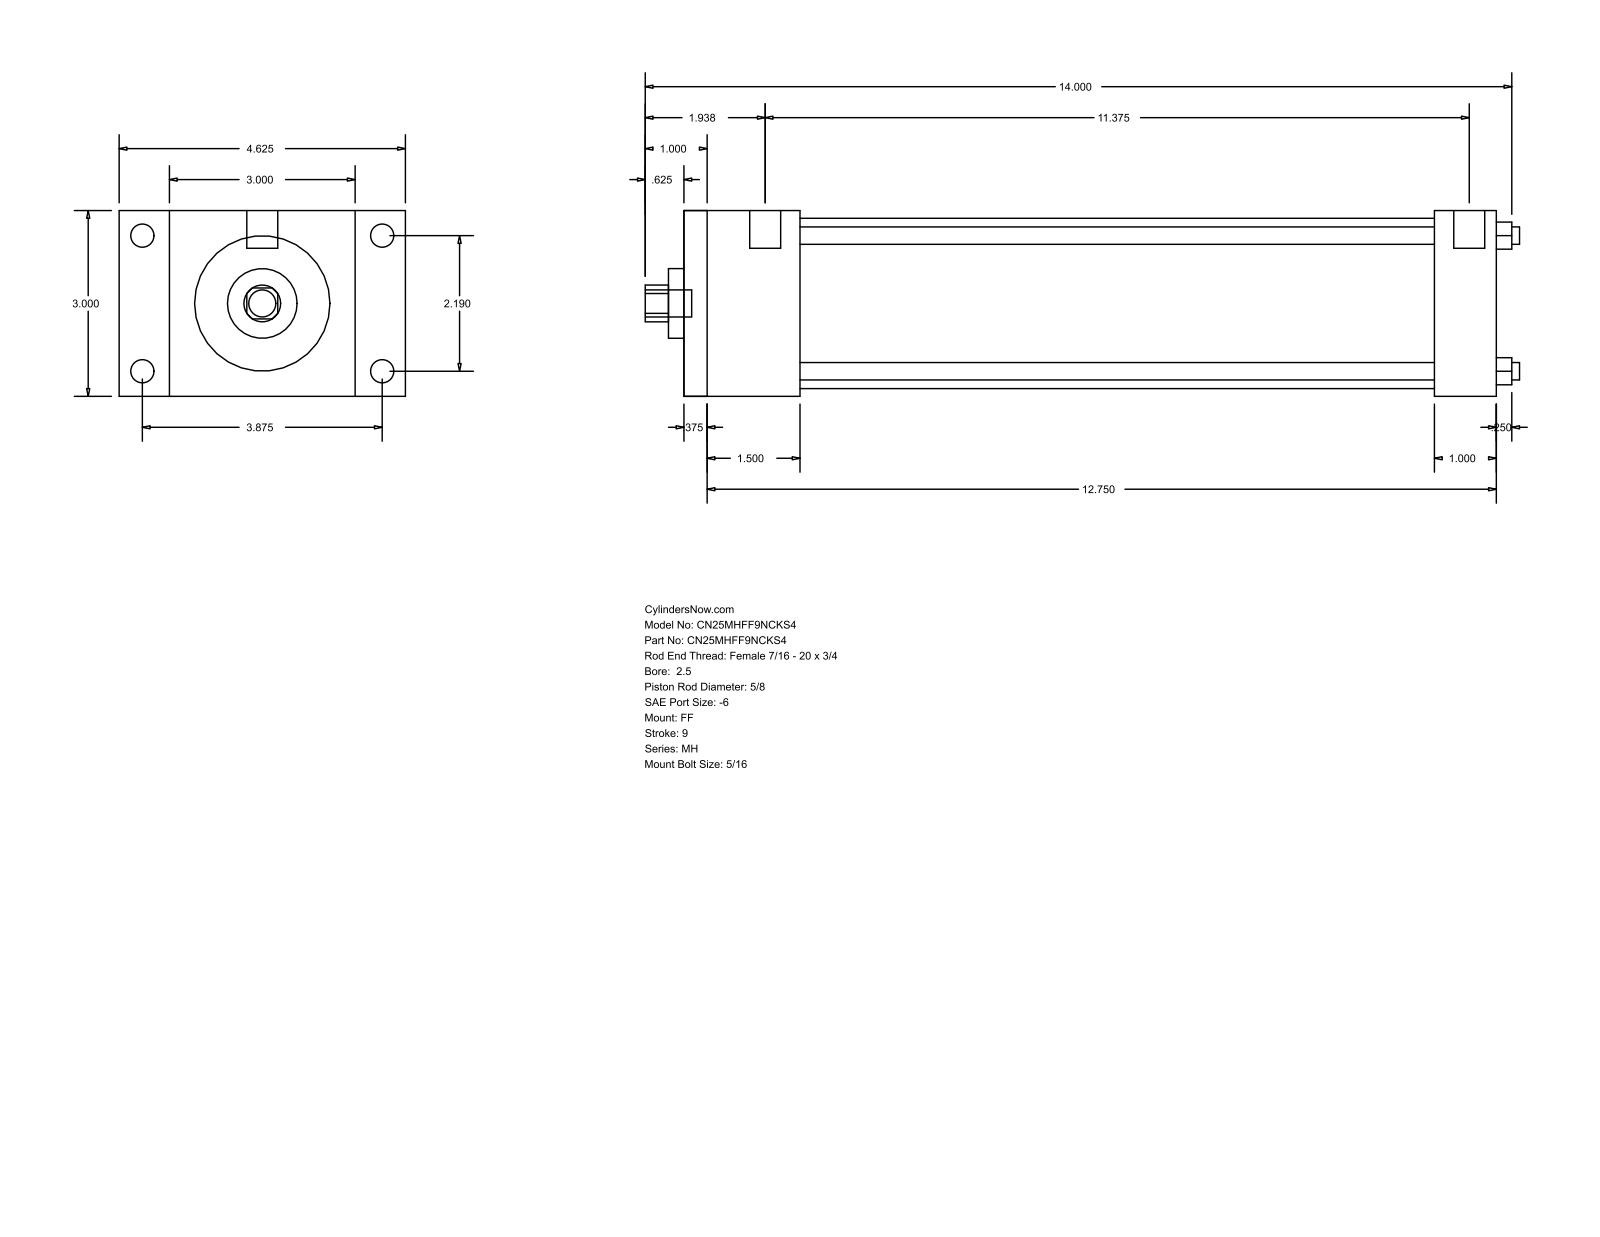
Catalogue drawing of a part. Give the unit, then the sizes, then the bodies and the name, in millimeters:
Units: millimetres
Overall size (bounding box): 358.77 × 117.47 × 76.2
Round holes (diameter × count): ⌀7.14 ×4, ⌀15.88 ×1, ⌀28.57 ×1, ⌀69.85 ×1
Round bosses / shafts (diameter × count): ⌀9.53 ×4, ⌀5.56 ×4, ⌀12.7 ×2, ⌀11.11 ×1
Partial cylindrical surfaces — rounded edges, fillets, slot ends (radius × count): R7.54 ×1
Main face-to-face distances: 76.2, 333.37, 9.52, 323.85, 25.4, 47.62, 307.97, 38.1, 298.45, 260.35
Hole centre spacings: 39.33, 55.62, 78.66
Bodies: 0 solids, 92 faces (64 planar, 28 cylindrical, 0 other)
Part name (STEP PRODUCT): MH_FF__0250_0.625
STEP written by: GSSL Pune (CONFIG_CONTROL_DESIGN)
